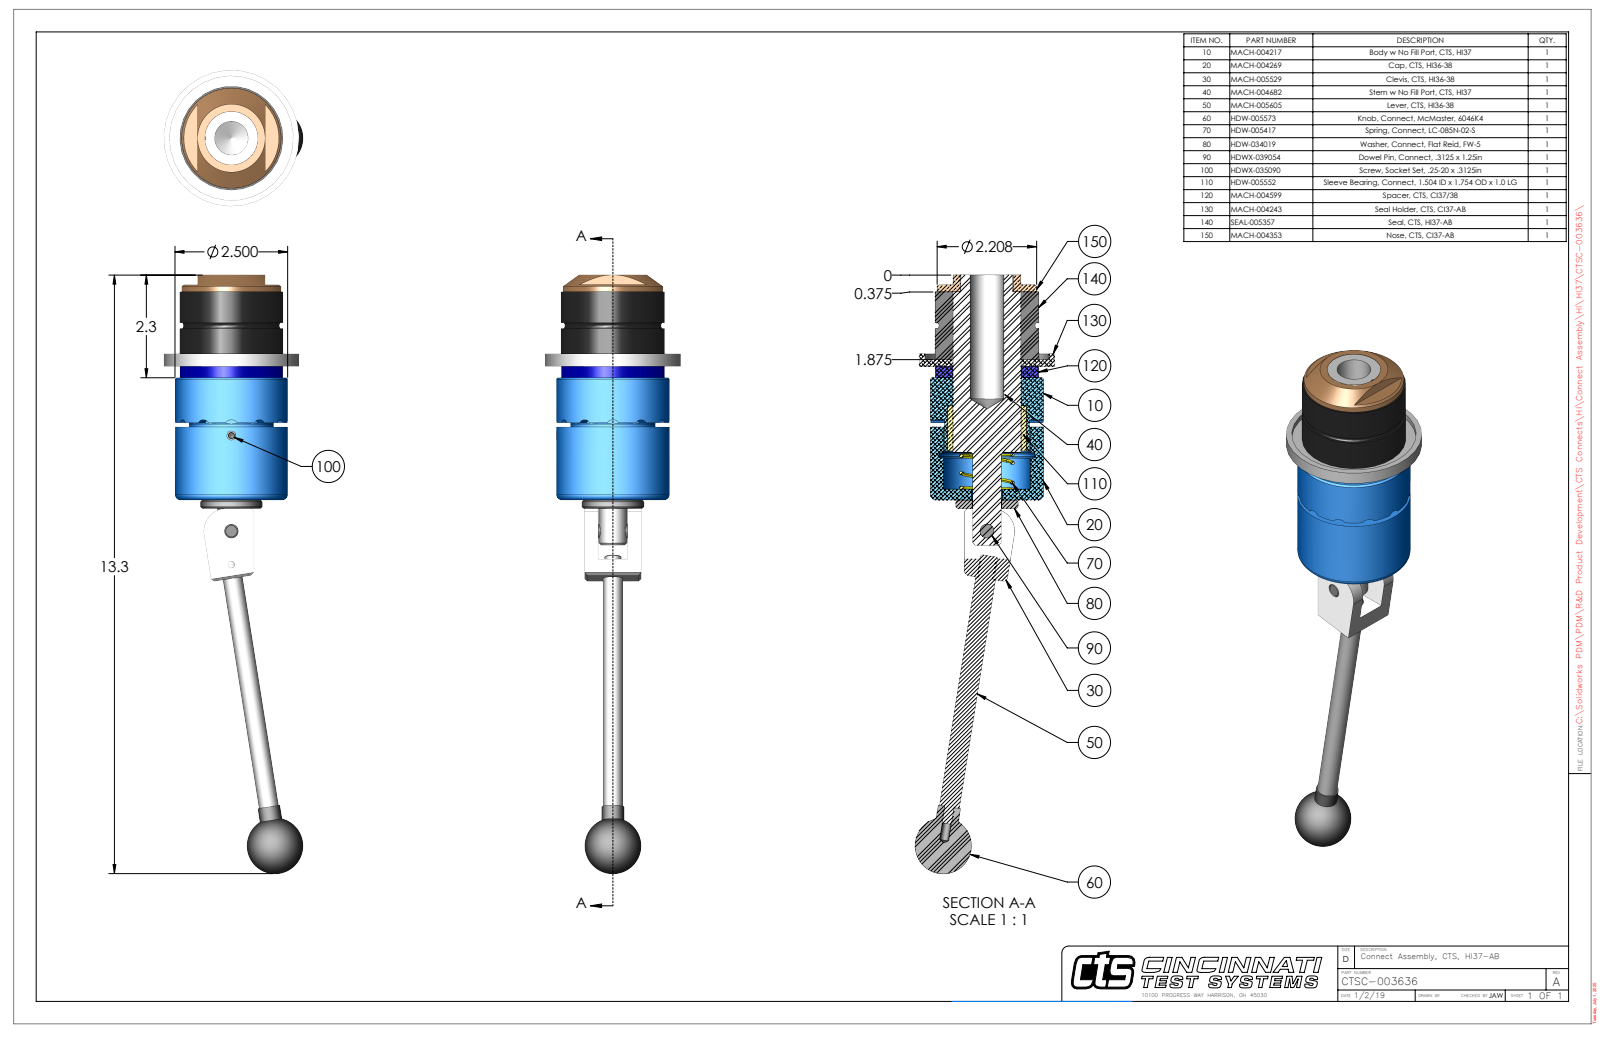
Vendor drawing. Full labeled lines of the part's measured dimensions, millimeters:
Part name (STEP PRODUCT): CTSC-003636
STEP written by: SolidWorks 2023 (AUTOMOTIVE_DESIGN)
Units: millimetres
Bodies: 10 solids, 279 faces (98 planar, 112 cylindrical, 69 other)
Overall size (bounding box): 337.2 × 78.6 × 76.2
Volume: 407 900 mm³ · Surface area: 90 260 mm²
Round holes (diameter × count): ⌀5.1 ×2, ⌀3.8 ×1, ⌀7.9 ×1, ⌀8 ×1, ⌀8 ×1, ⌀16.7 ×1, ⌀17.7 ×1, ⌀19.1 ×1, ⌀29.8 ×1, ⌀38 ×1, ⌀38.1 ×1, ⌀38.4 ×1
Round bosses / shafts (diameter × count): ⌀76.2 ×1, ⌀63.5 ×1, ⌀58.3 ×1, ⌀57.9 ×1, ⌀56.1 ×1, ⌀47.6 ×1, ⌀38.1 ×1, ⌀38 ×1
Partial cylindrical surfaces — rounded edges, fillets, slot ends (radius × count): R3 ×12, R0.7 ×2, R12.7 ×1, R30.8 ×1
Main face-to-face distances: 3.9, 38.1, 42, 6.4, 10.2, 48.3, 68.9, 75.3, 79.1, 117.2
Hole centre spacings: 18.8, 53.8, 72.6
